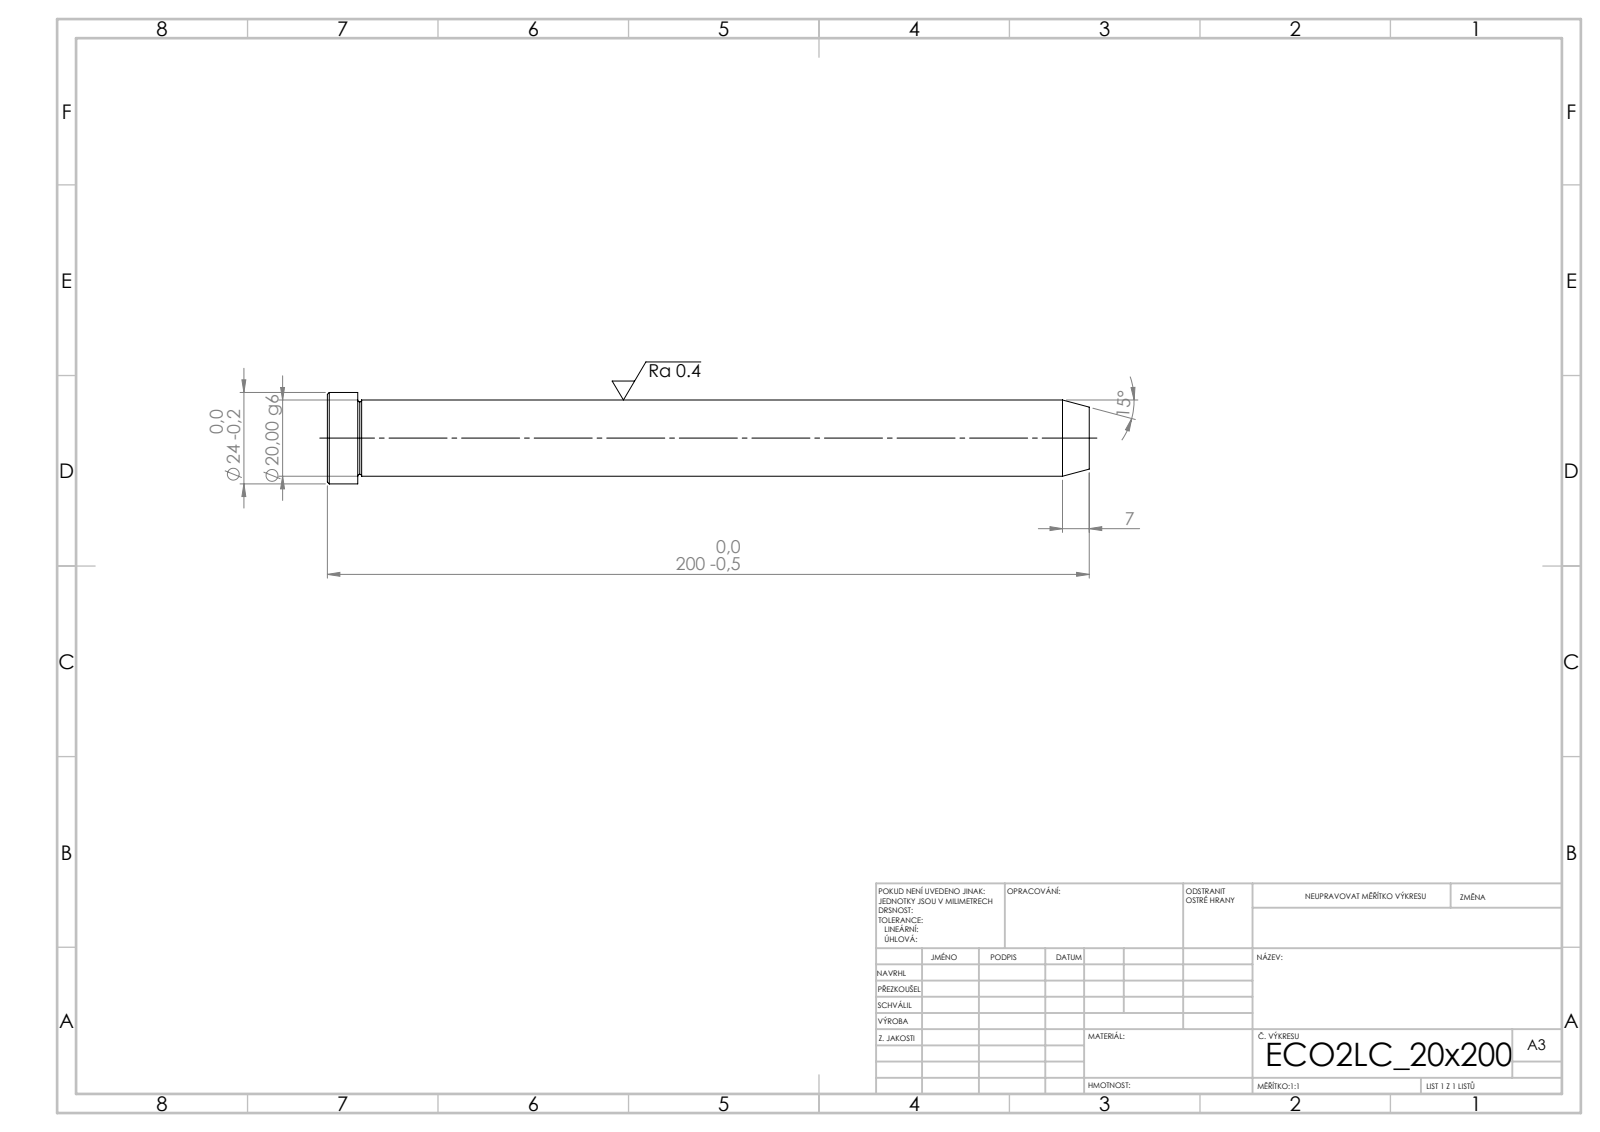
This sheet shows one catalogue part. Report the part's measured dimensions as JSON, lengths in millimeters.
{"step_written_by": "SolidWorks 2019 (CONFIG_CONTROL_DESIGN)", "units": "millimeters", "bodies": {"solids": 1, "faces": 15, "planar": 3, "cylindrical": 4, "other": 8}, "overall_size": [200, 24, 24], "volume_mm3": 63518, "surface_area_mm2": 13448, "round_bosses_or_shafts": [[24, 1], [20, 1]], "face_to_face_distances": [200, 192, 8]}
